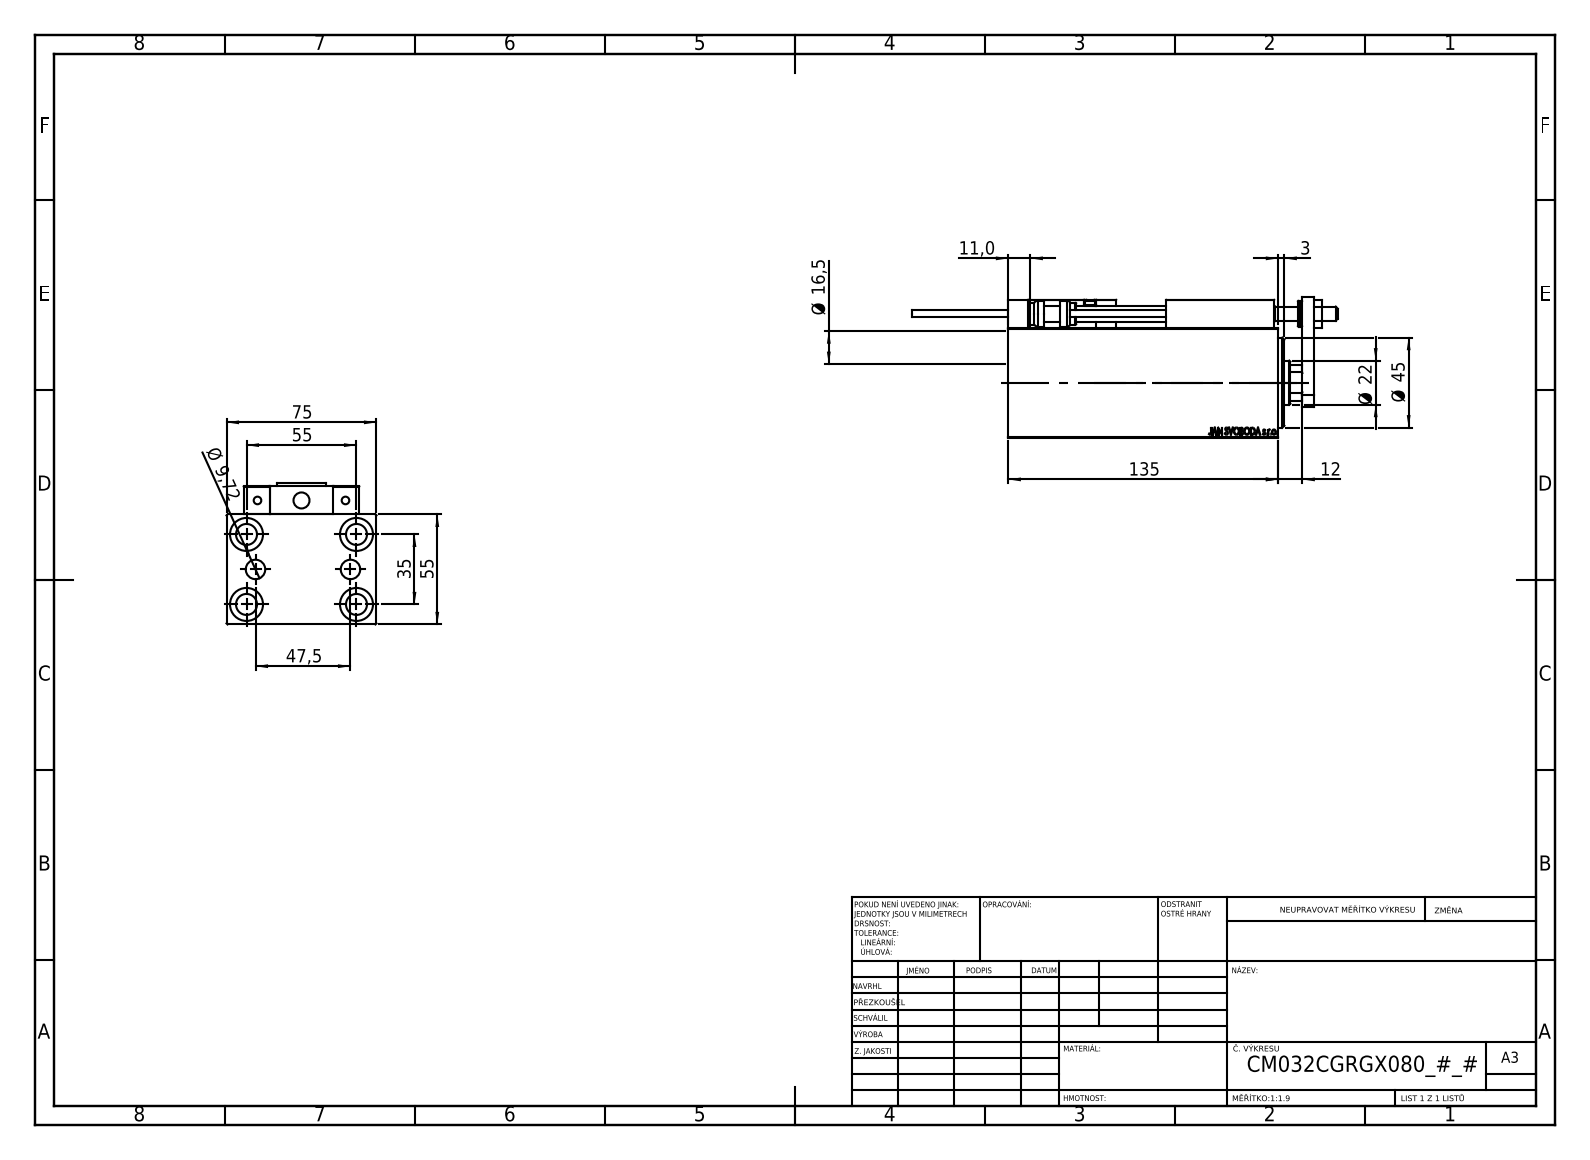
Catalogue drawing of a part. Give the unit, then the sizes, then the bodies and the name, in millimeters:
Units: millimetres
Overall size (bounding box): 212.7 × 75 × 70.5
Round holes (diameter × count): ⌀8 ×5, ⌀10.5 ×5, ⌀16.5 ×5, ⌀3.2 ×4, ⌀4 ×4, ⌀5 ×2, ⌀9.72 ×2, ⌀7 ×1, ⌀22 ×1, ⌀25.5 ×1, ⌀32 ×1, ⌀34 ×1
Round bosses / shafts (diameter × count): ⌀5 ×2, ⌀3.8 ×2, ⌀13 ×1, ⌀11 ×1
Partial cylindrical surfaces — rounded edges, fillets, slot ends (radius × count): R0.3 ×30, R3 ×2, R10.5 ×1
Main face-to-face distances: 55, 75, 14, 10, 12, 69, 7, 25, 15, 5
Hole centre spacings: 32.6, 11.37, 17.76, 18.07, 20, 29.59, 29.69, 32.33
Volume: 519 768 mm³ · Surface area: 118 998 mm²
Bodies: 23 solids, 1272 faces (558 planar, 180 cylindrical, 534 other)
Part name (STEP PRODUCT): V450CM_C_VCP; SWITCH DIM B,W; V450CM_VC_B; V450CM_C_Body (+7 more)
STEP written by: SolidWorks 2019 (CONFIG_CONTROL_DESIGN)
